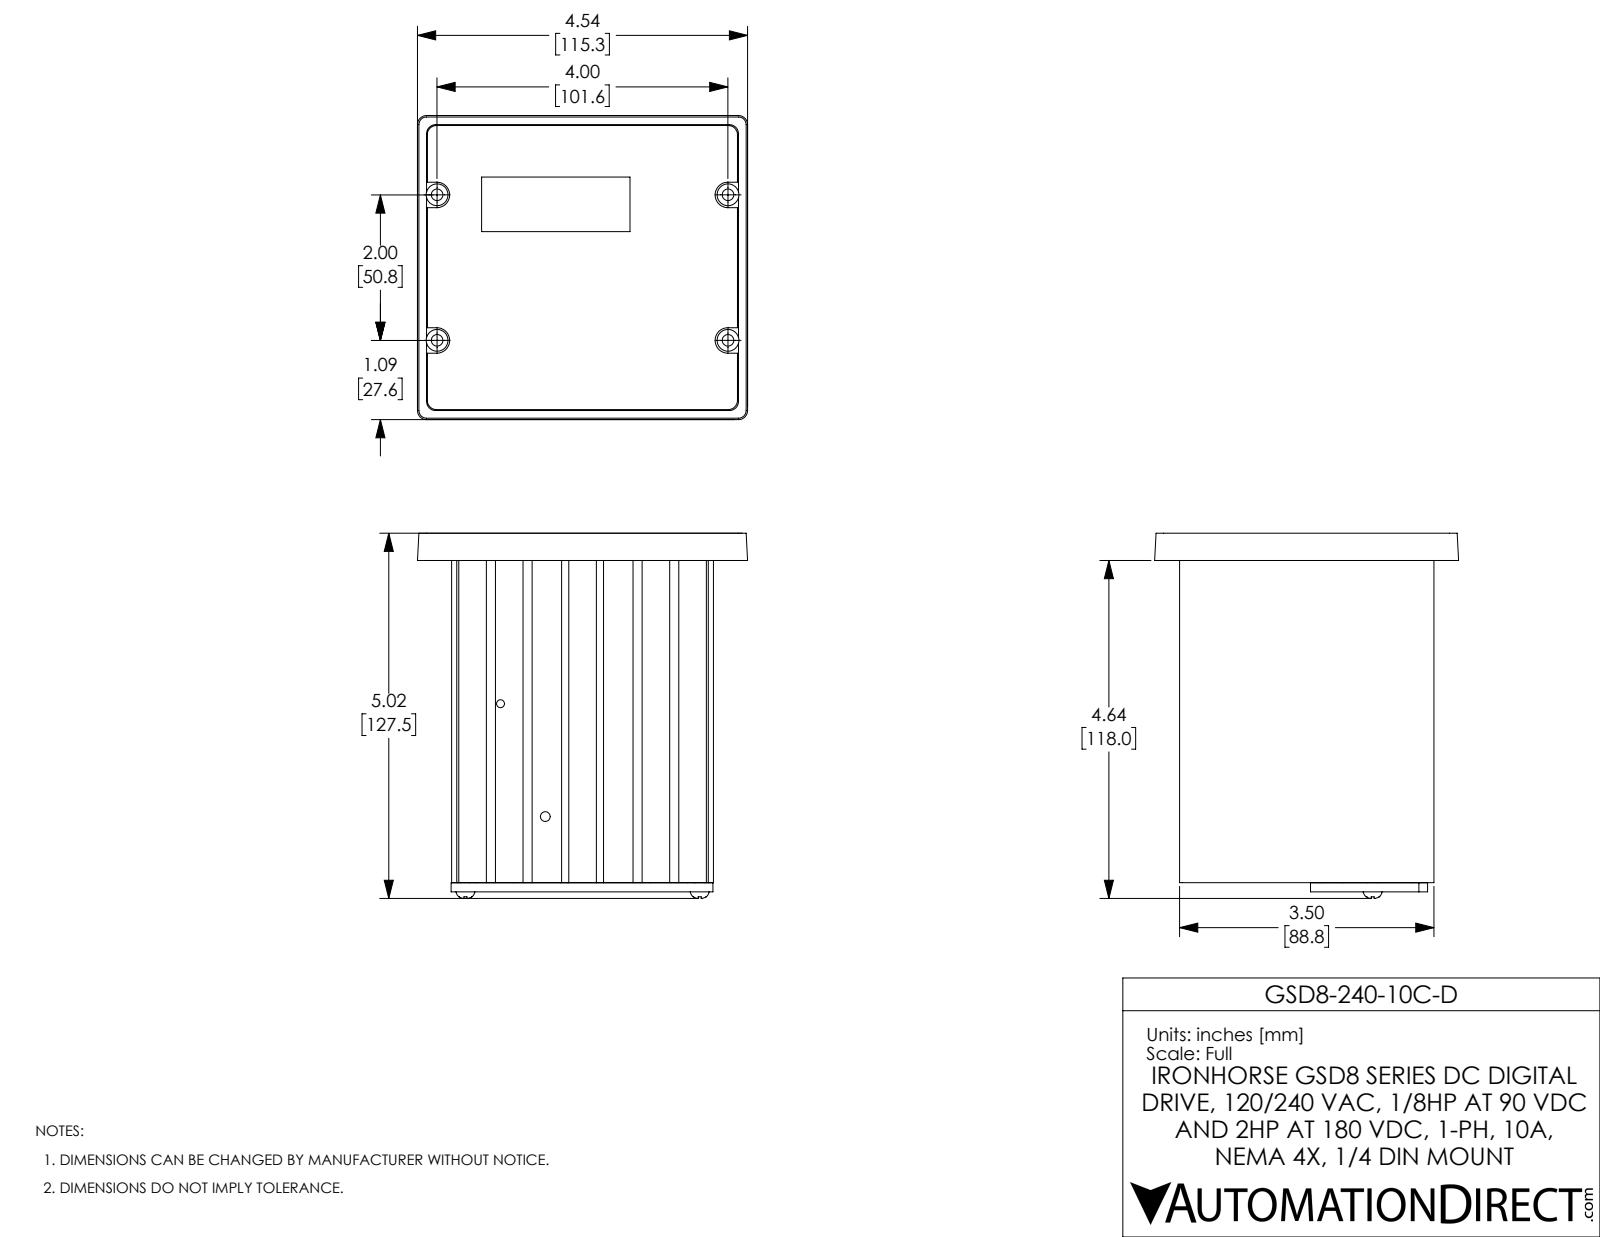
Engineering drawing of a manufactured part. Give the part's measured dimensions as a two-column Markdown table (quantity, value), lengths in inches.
| quantity | value |
| --- | --- |
| part name | GSD8-240-10C-D |
| STEP written by | SolidWorks 2017 (AUTOMOTIVE_DESIGN) |
| units | inches |
| bodies | 15 solids, 2177 faces (1186 planar, 918 cylindrical, 73 other) |
| overall size | 5.019 × 4.539 × 4.179 |
| volume | 17.99 in³ |
| surface area | 384.8 in² |
| round holes (diameter × count) | 0.033 × 50, 0.04 × 39, 0.02 × 32, 0.055 × 29, 0.035 × 27, 0.028 × 16, 0.016 × 12, 0.157 × 12, 0.028 × 11, 0.033 × 10, 0.035 × 10, 0.16 × 10 |
| round bosses / shafts (diameter × count) | 0.02 × 36, 0.247 × 3, 0.134 × 3 |
| partial cylindrical surfaces (radius × count) | 0.05 × 18, 0.039 × 16, 0.125 × 12, 0.126 × 10, 0.036 × 8, 0.175 × 7, 0.035 × 4, 0.045 × 4 |
| main face-to-face distances | 0.504, 1.513, 0.15, 2.017, 1.008, 2.521, 0.062, 3.6, 0.045, 1.734 |
| hole center spacings | 0.1, 0.2, 0.6, 0.608, 0.3, 0.632, 0.4, 0.671 |
